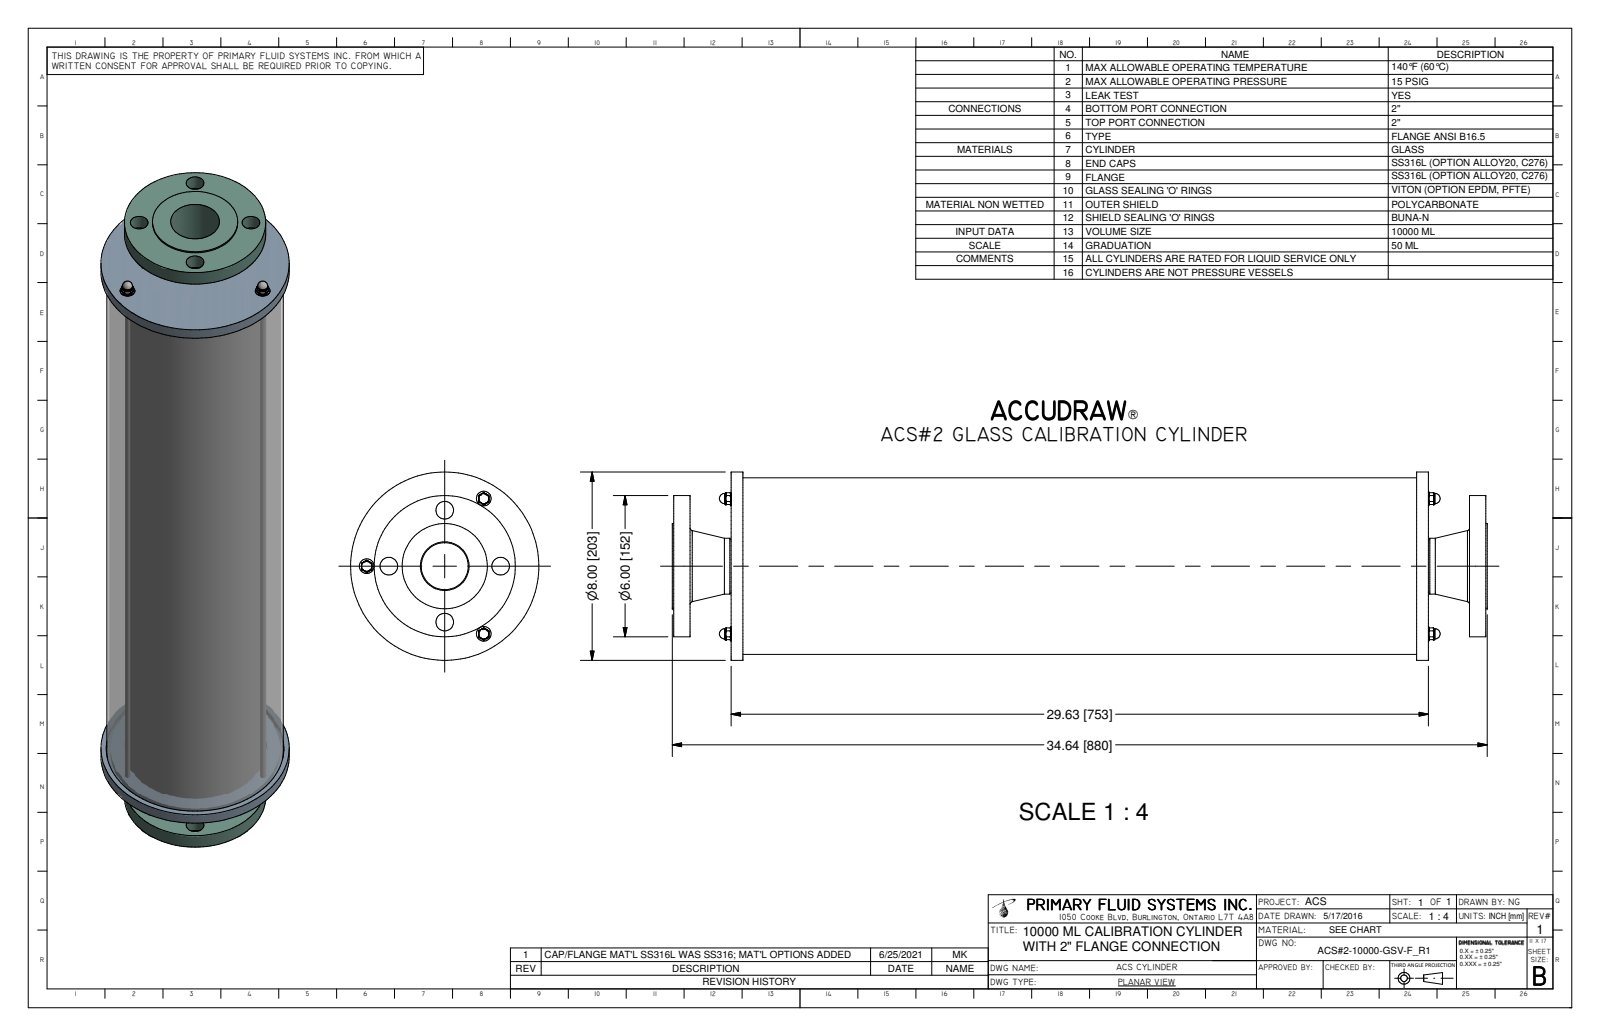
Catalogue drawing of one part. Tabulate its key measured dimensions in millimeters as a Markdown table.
| quantity | value |
| --- | --- |
| part name | ACS#2-10000-GSV-F_R0; ACS-3-10000-METAL-S_R1; ACS-2-10000_R6; ACS-1-10000-A_R0 (+4 more) |
| STEP written by | Autodesk Inventor 2009 (AUTOMOTIVE_DESIGN) |
| units | millimeters |
| bodies | 21 solids, 455 faces (46 planar, 57 cylindrical, 352 other) |
| overall size | 879.7 × 203.2 × 203.2 |
| volume | 4 449 000 mm³ |
| surface area | 1 899 000 mm² |
| round holes (diameter × count) | 19.1 × 4, 4.6 × 3, 6.8 × 3, 7.1 × 3, 52.5 × 1, 140 × 1, 154.1 × 1, 184.2 × 1, 191.8 × 1 |
| round bosses / shafts (diameter × count) | 15.9 × 3, 6.4 × 3, 203.2 × 1, 190.5 × 1, 182.9 × 1, 152.4 × 1, 150 × 1, 137.8 × 1 |
| main face-to-face distances | 752.6, 44.5, 797.1, 57.2, 784.4, 12.7, 739.9, 17.5, 62, 74.7 |
| hole center spacings | 60.3, 85.3, 84.3, 44, 75.2, 103.6, 120.7, 125.8 |
